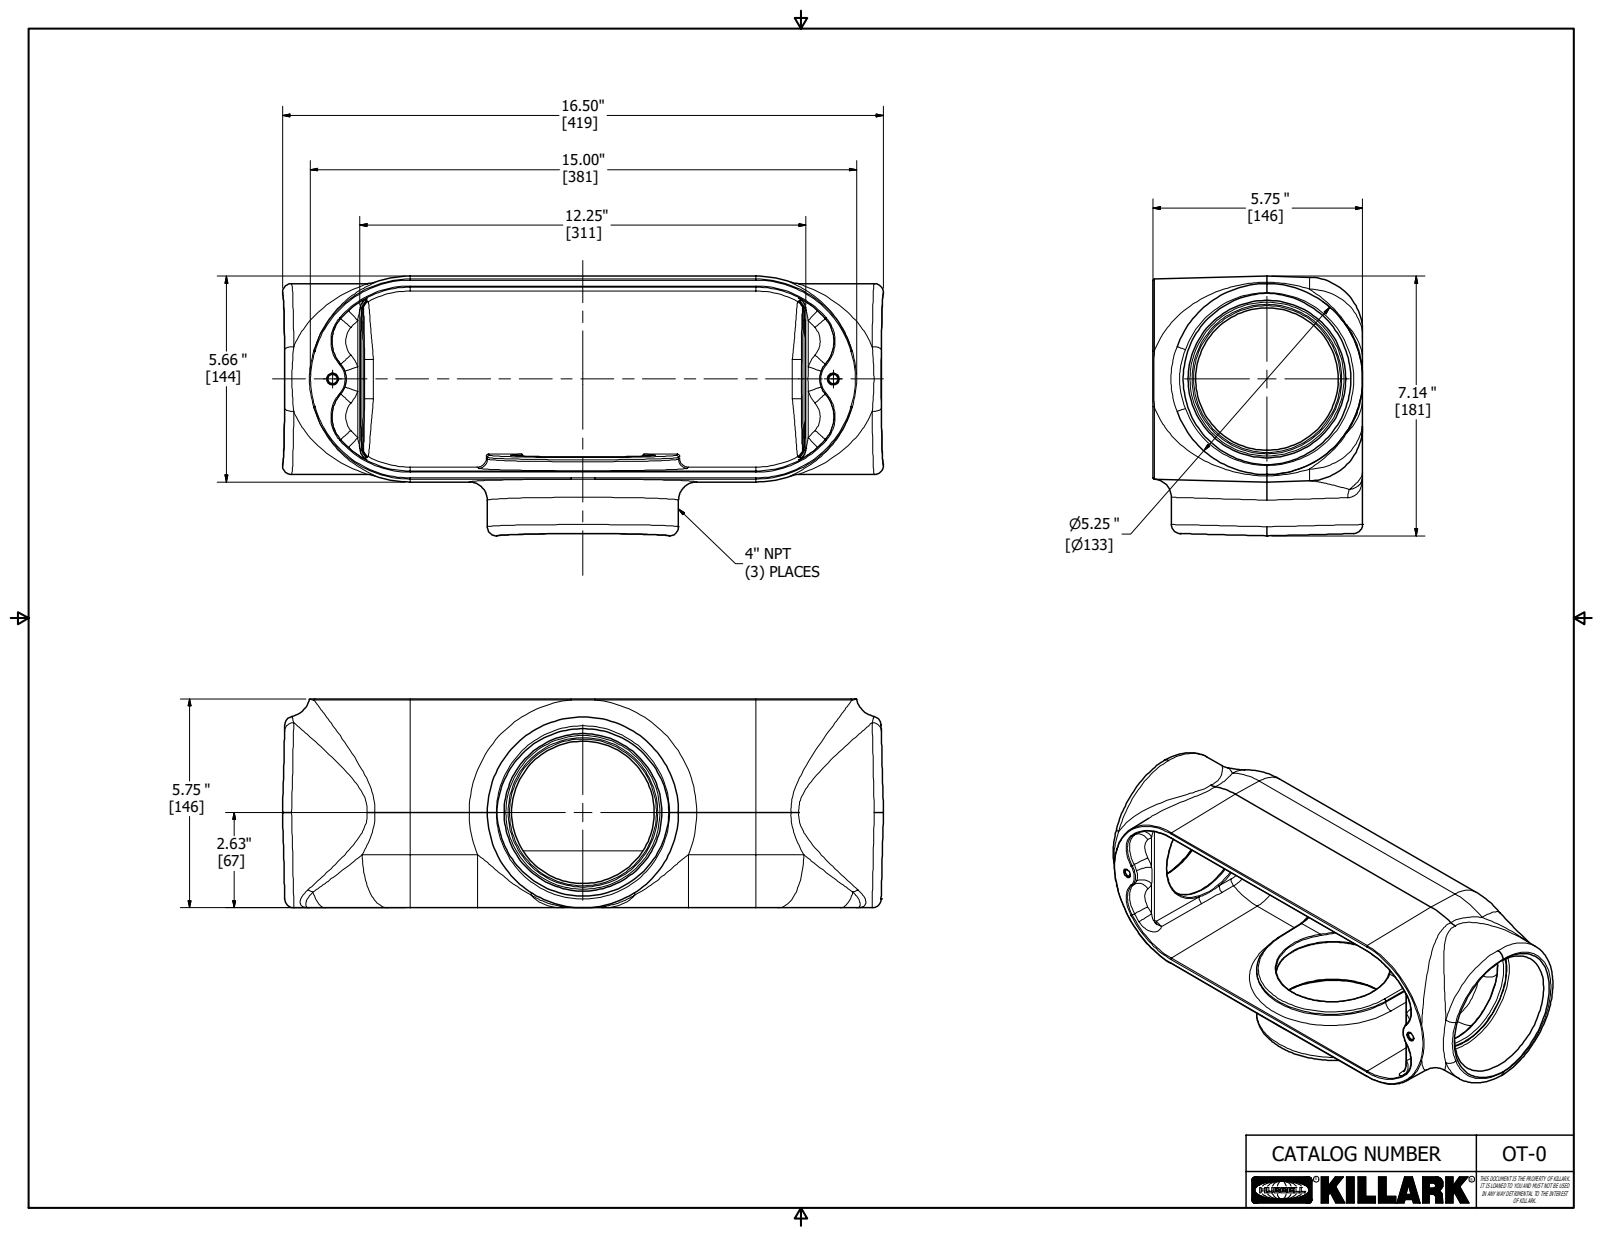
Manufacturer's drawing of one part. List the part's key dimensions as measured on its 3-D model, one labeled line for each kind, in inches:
Part name (STEP PRODUCT): 10756-1 OT-0
STEP written by: Autodesk Inventor 2018 (AUTOMOTIVE_DESIGN)
Units: inches
Bodies: 1 solid, 1406 faces (721 planar, 81 cylindrical, 604 other)
Overall size (bounding box): 16.5 × 7.144 × 5.75
Volume: 113.8 in³ · Surface area: 569.4 in²
Round holes (diameter × count): ⌀3.914 ×2, ⌀0.502 ×1
Round bosses / shafts (diameter × count): ⌀5.25 ×2, ⌀0.752 ×1
Partial cylindrical surfaces — rounded edges, fillets, slot ends (radius × count): R0.031 ×28, R0.25 ×4, R1.281 ×3, R0.06 ×2, R0.062 ×2, R0.625 ×2, R1.5 ×2, R0.031 ×1
Main face-to-face distances: 5.281, 0.313, 0.382, 5.663, 5.75, 5.437, 0.375, 0.358, 4.923, 0.062
